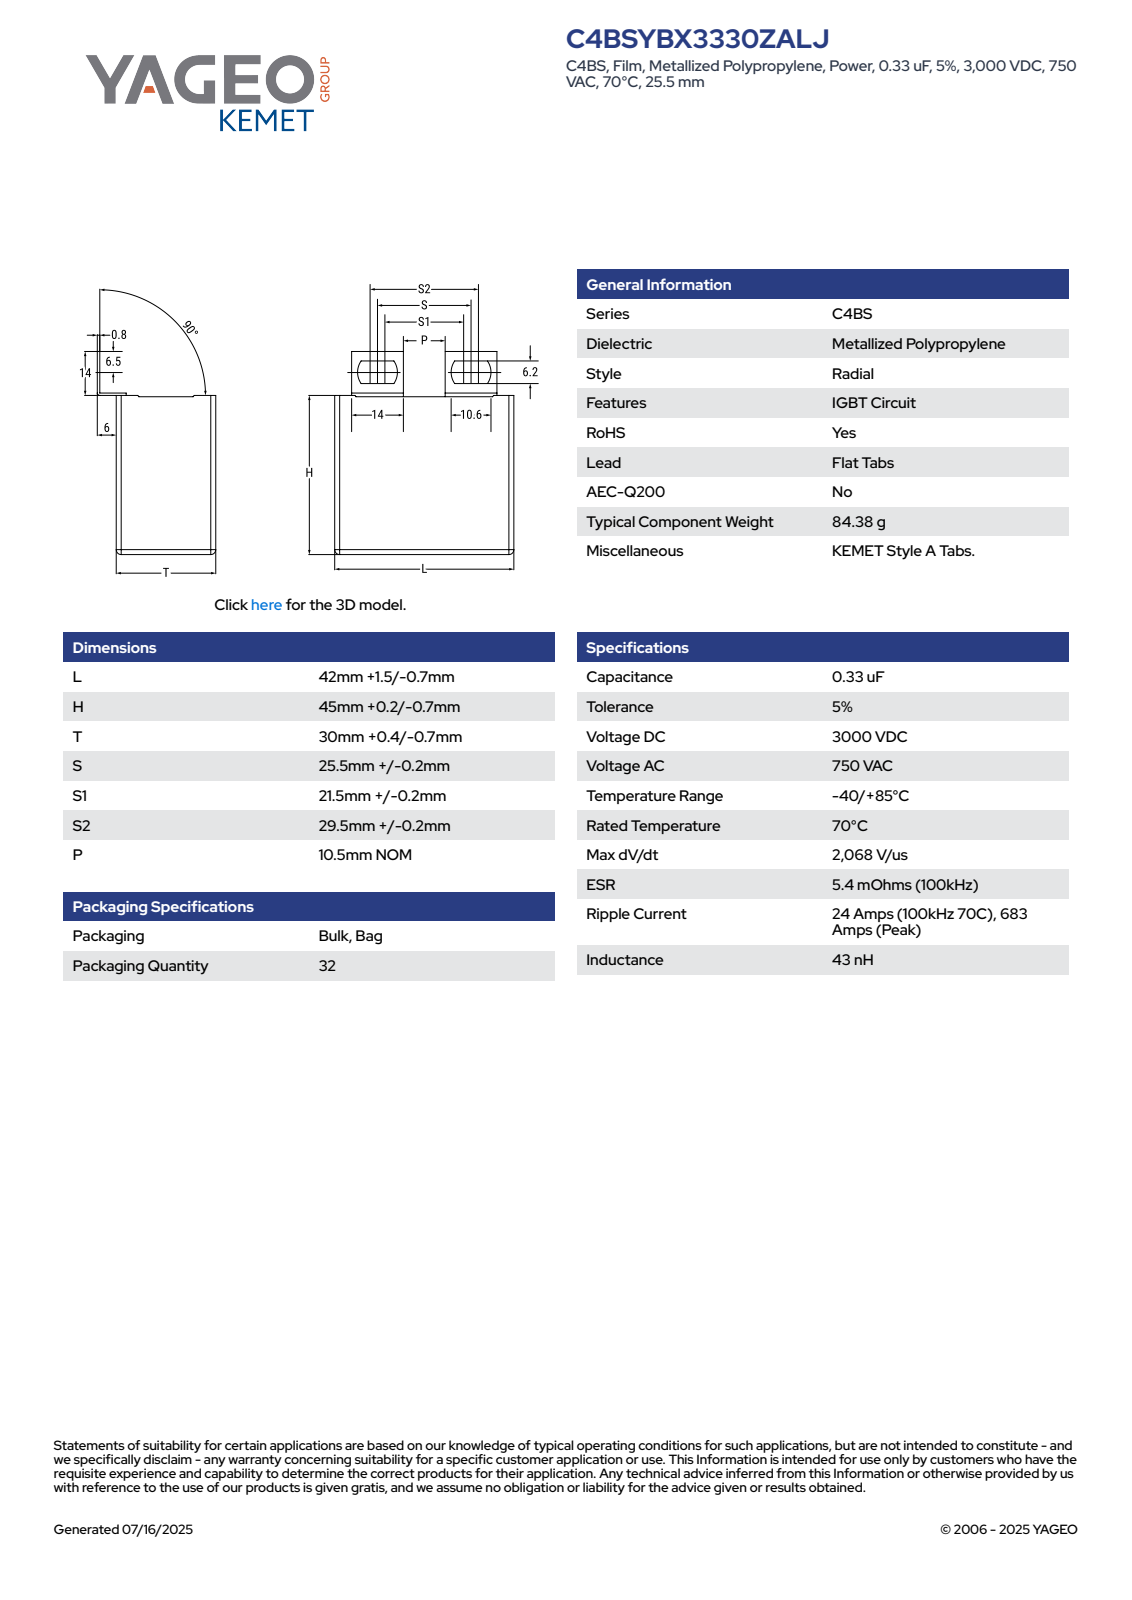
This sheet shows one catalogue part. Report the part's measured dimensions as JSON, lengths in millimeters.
{"part_name": "CFP_C4BA_42X45X30_L43.5H45.2T30.4S25.7", "step_written_by": "SolidWorks 2014 (AUTOMOTIVE_DESIGN)", "units": "millimeters", "bodies": {"solids": 4, "faces": 97, "planar": 91, "cylindrical": 6, "other": 0}, "overall_size": [59.8, 43.5, 36.41], "volume_mm3": 60147, "surface_area_mm2": 11066, "partial_cylinders_radius": [[6.1, 4]], "face_to_face_distances": [30.4, 43.5, 45.15, 0.6, 45.2, 45.8, 0.65, 36.4, 6, 35.8]}
